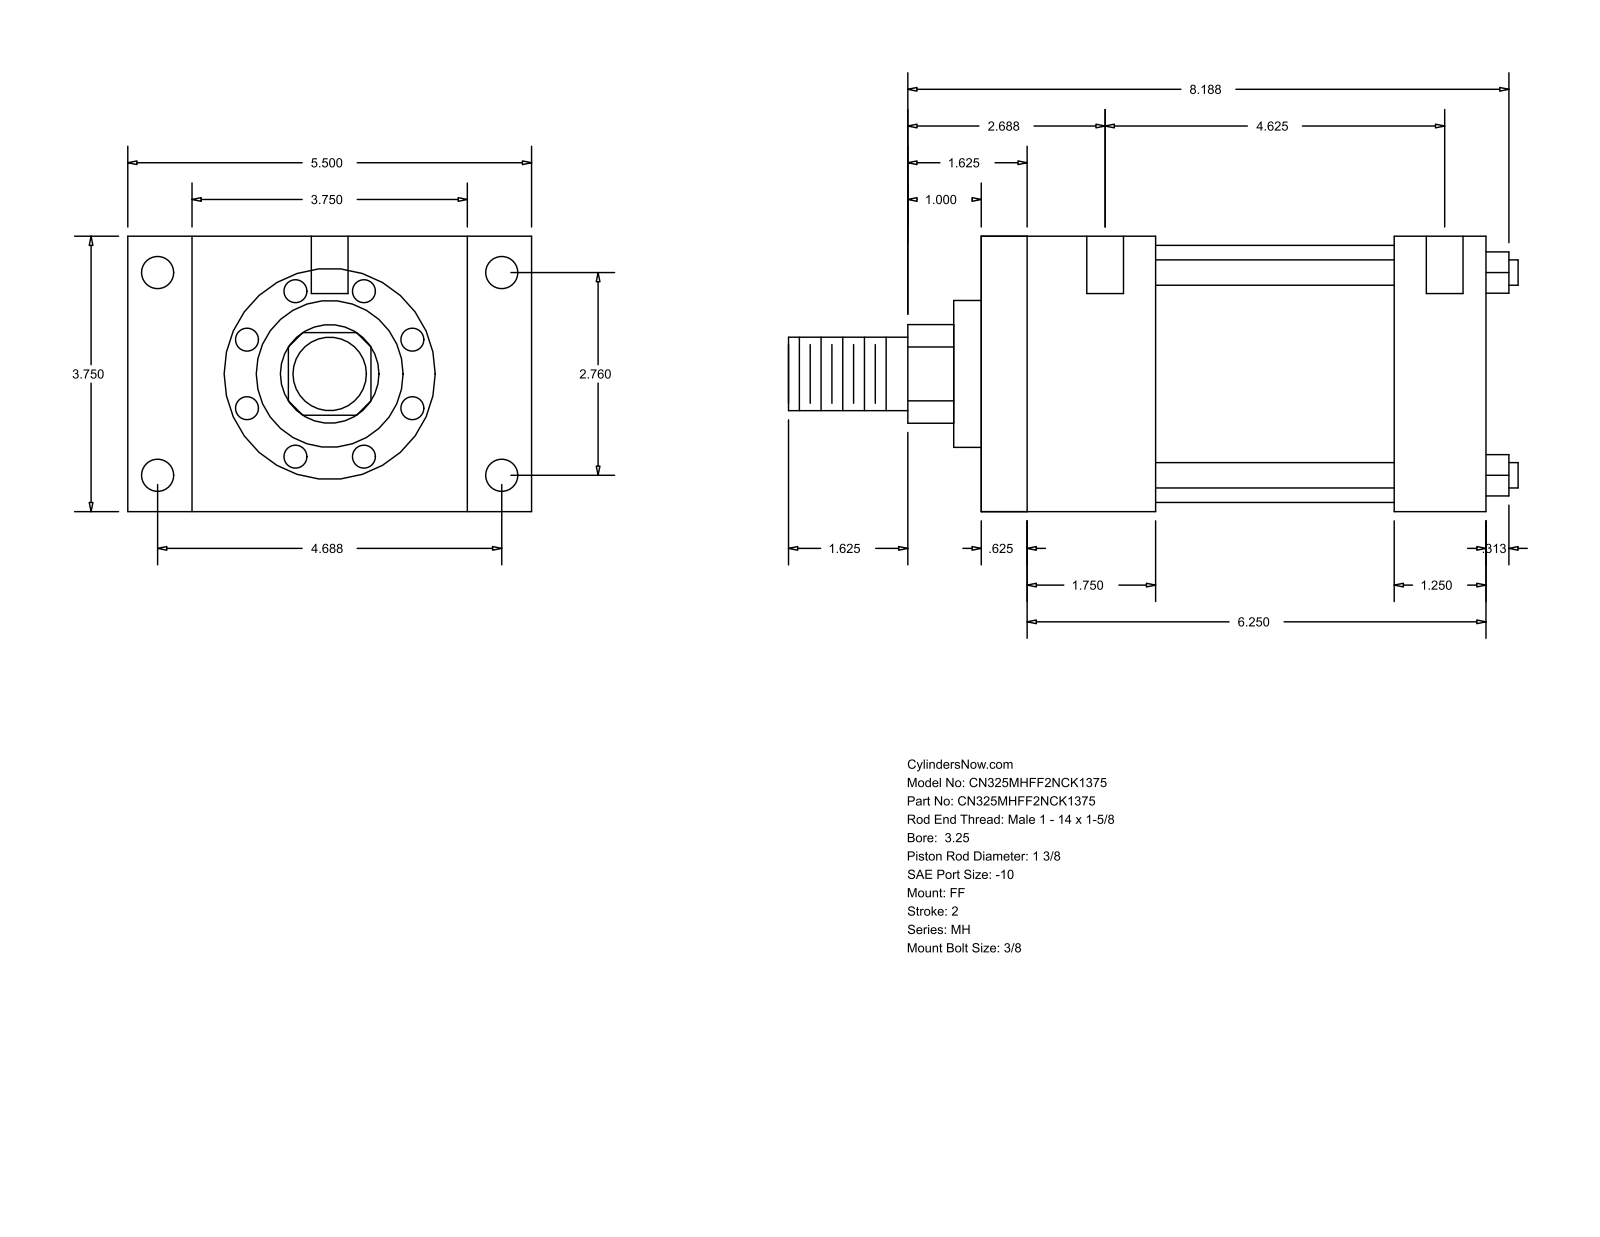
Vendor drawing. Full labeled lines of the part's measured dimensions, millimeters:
Part name (STEP PRODUCT): MH_FF__0325_1.375
STEP written by: GSSL Pune (CONFIG_CONTROL_DESIGN)
Units: millimetres
Bodies: 0 solids, 92 faces (64 planar, 28 cylindrical, 0 other)
Overall size (bounding box): 252.41 × 139.7 × 95.25
Round holes (diameter × count): ⌀5.56 ×4, ⌀11.13 ×4, ⌀12.7 ×2
Round bosses / shafts (diameter × count): ⌀8.76 ×4, ⌀88.9 ×1, ⌀50.8 ×1, ⌀34.92 ×1, ⌀25.4 ×1
Partial cylindrical surfaces — rounded edges, fillets, slot ends (radius × count): R17.06 ×1
Main face-to-face distances: 95.24, 174.63, 15.87, 158.76, 22.23, 117.47, 142.88, 127.01, 31.75, 60.32
Hole centre spacings: 70.1, 119.06, 123.83, 138.16, 1.59, 4.76, 117.48, 119.07
